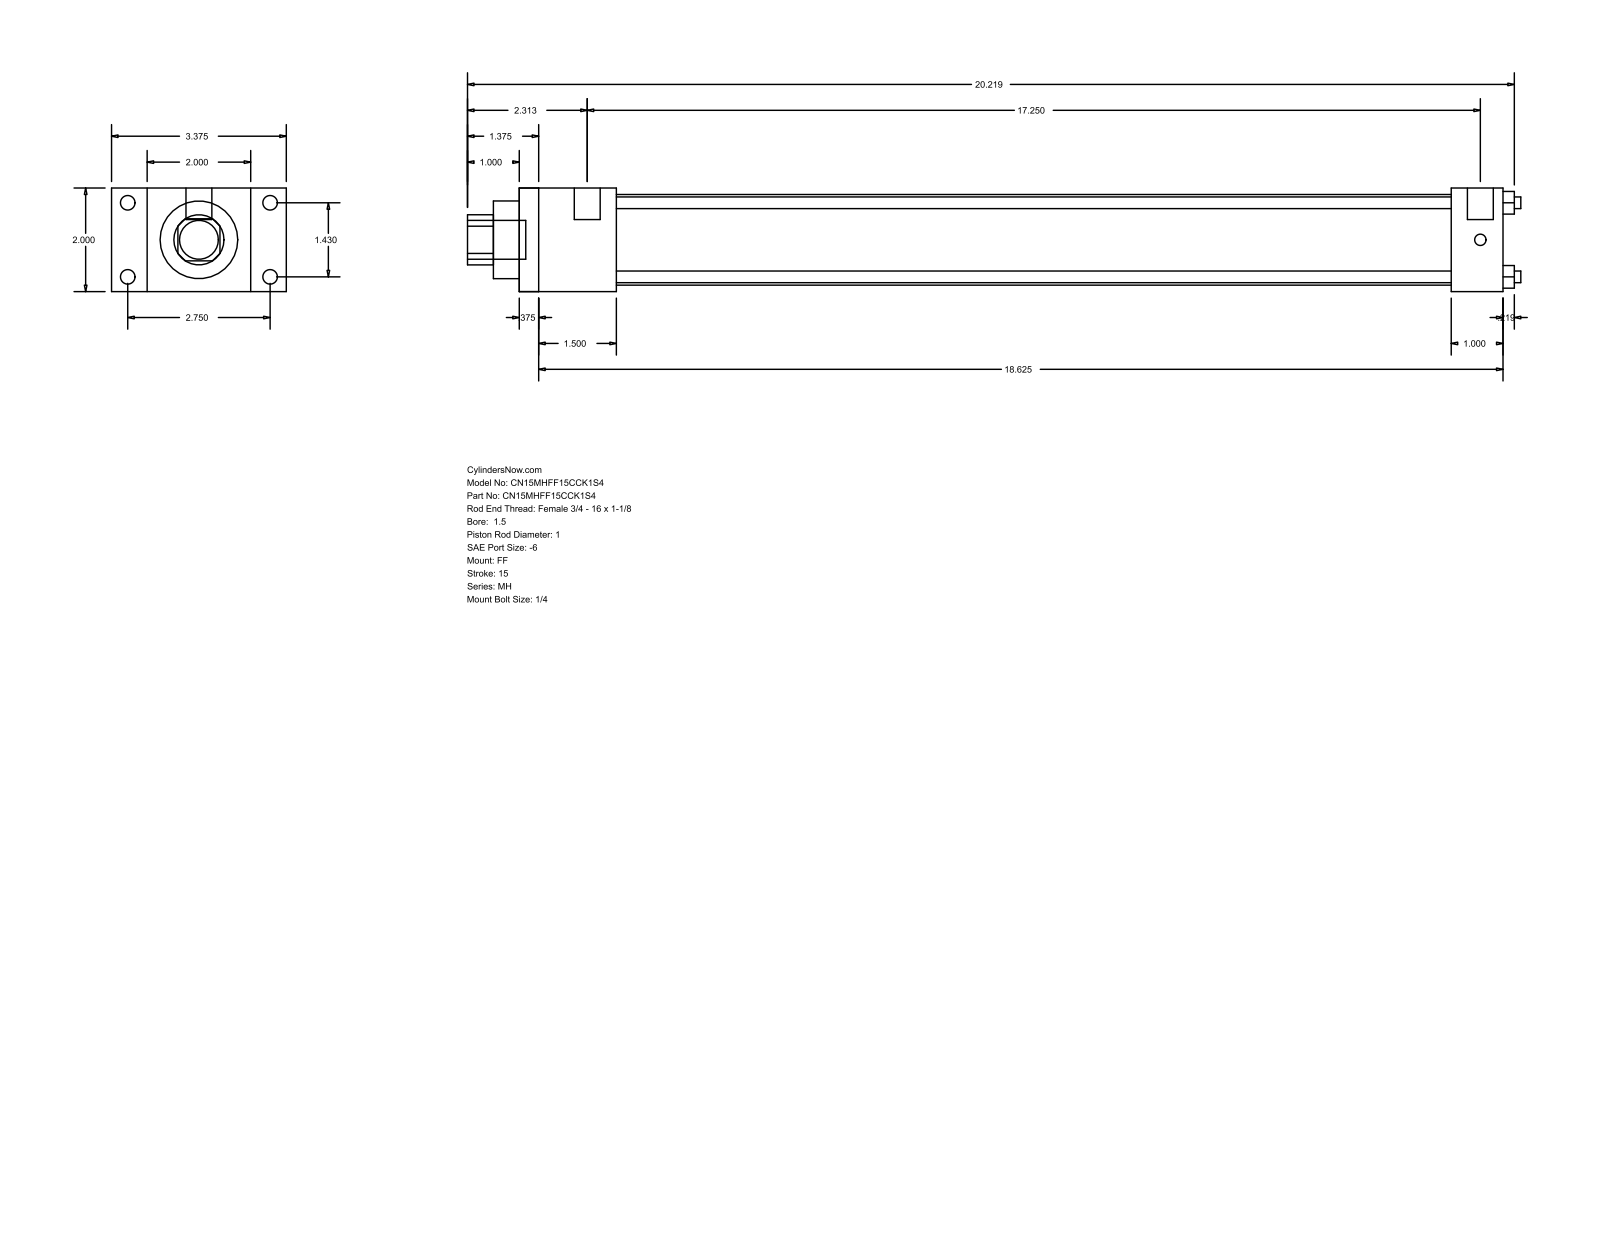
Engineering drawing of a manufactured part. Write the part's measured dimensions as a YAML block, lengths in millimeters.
part_name: "MH_FF__0150_1"
step_written_by: "GSSL Pune (CONFIG_CONTROL_DESIGN)"
units: millimeters
bodies: {solids: 0, faces: 92, planar: 64, cylindrical: 28, other: 0}
overall_size: [516.73, 85.72, 50.8]
round_holes:
  - {diameter: 5.71, count: 4}
  - {diameter: 25.4, count: 1}
  - {diameter: 38.1, count: 1}
  - {diameter: 44.45, count: 1}
round_bosses_or_shafts:
  - {diameter: 7.14, count: 4}
  - {diameter: 5.56, count: 4}
  - {diameter: 12.7, count: 2}
  - {diameter: 19.05, count: 1}
partial_cylinders:
  - {radius: 12.29, count: 1}
face_to_face_distances: [50.8, 482.6, 9.52, 473.08, 25.4, 17.46, 68.26, 47.63, 38.11, 434.97]
hole_center_spacings: [25.68, 36.32, 51.36]
